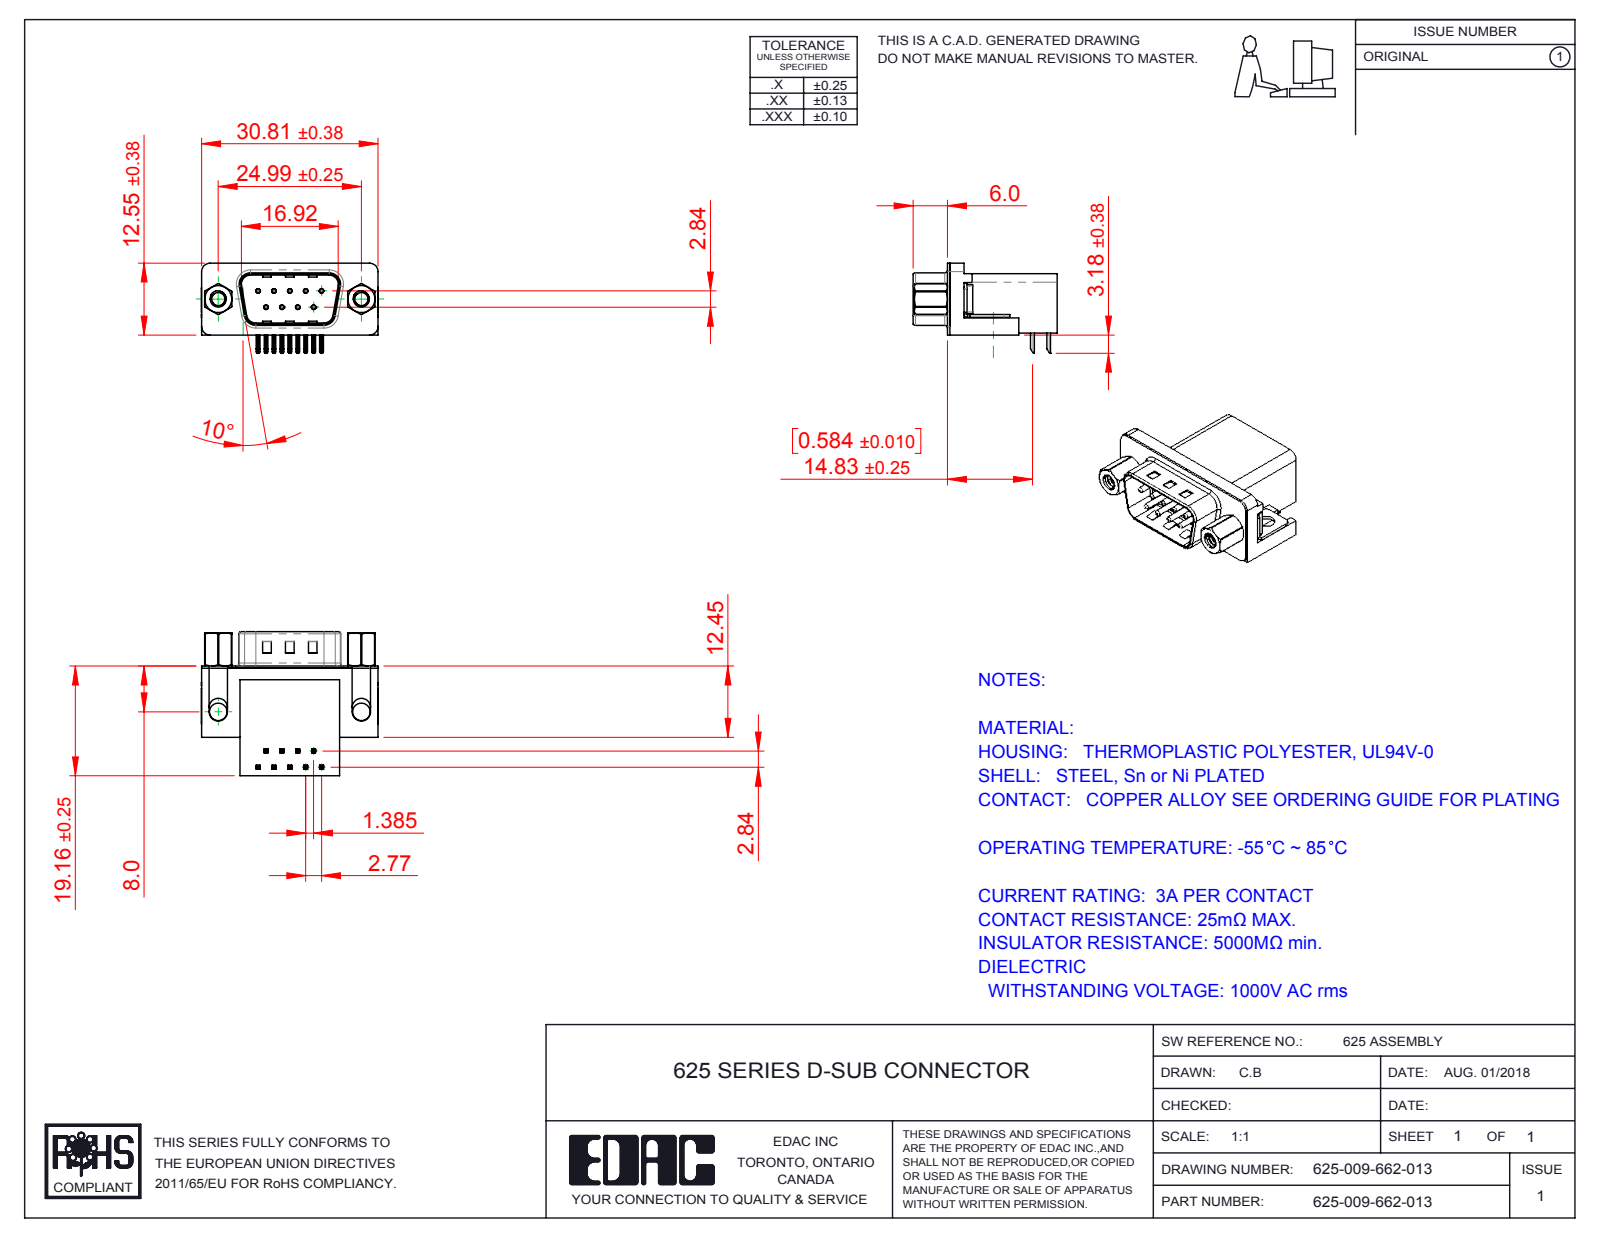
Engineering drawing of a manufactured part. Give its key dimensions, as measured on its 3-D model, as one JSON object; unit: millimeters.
{"part_name": "625 Thru Hole Board Mount; 625 Shell_9 Socket; 625 Housing_9 Socket; 625 Contact Top (+4 more)", "step_written_by": "SolidWorks 2016 (CONFIG_CONTROL_DESIGN)", "units": "millimeters", "bodies": {"solids": 17, "faces": 1119, "planar": 595, "cylindrical": 389, "other": 135}, "overall_size": [30.89, 25.16, 15.73], "volume_mm3": 4686, "surface_area_mm2": 5421, "round_holes": [[0.35, 9], [0.8, 9], [2.26, 2], [2.29, 2], [3.05, 2], [4, 2], [4.8, 2], [5, 2]], "round_bosses_or_shafts": [[0.75, 9], [4.9, 2], [4.75, 2], [3.9, 2], [2.79, 2]], "partial_cylinders_radius": [[0.25, 44], [0.12, 18], [1, 16], [0.5, 9], [1.5, 8], [1.6, 8], [0.9, 4], [2, 4]], "face_to_face_distances": [0.4, 10.34, 18.76, 19.16, 16.26, 2.5, 2.9, 0.5, 0.35, 10.69], "hole_center_spacings": [3.16, 2.77, 5.54, 5.03, 5.04, 8.31, 7.48, 7.49]}
